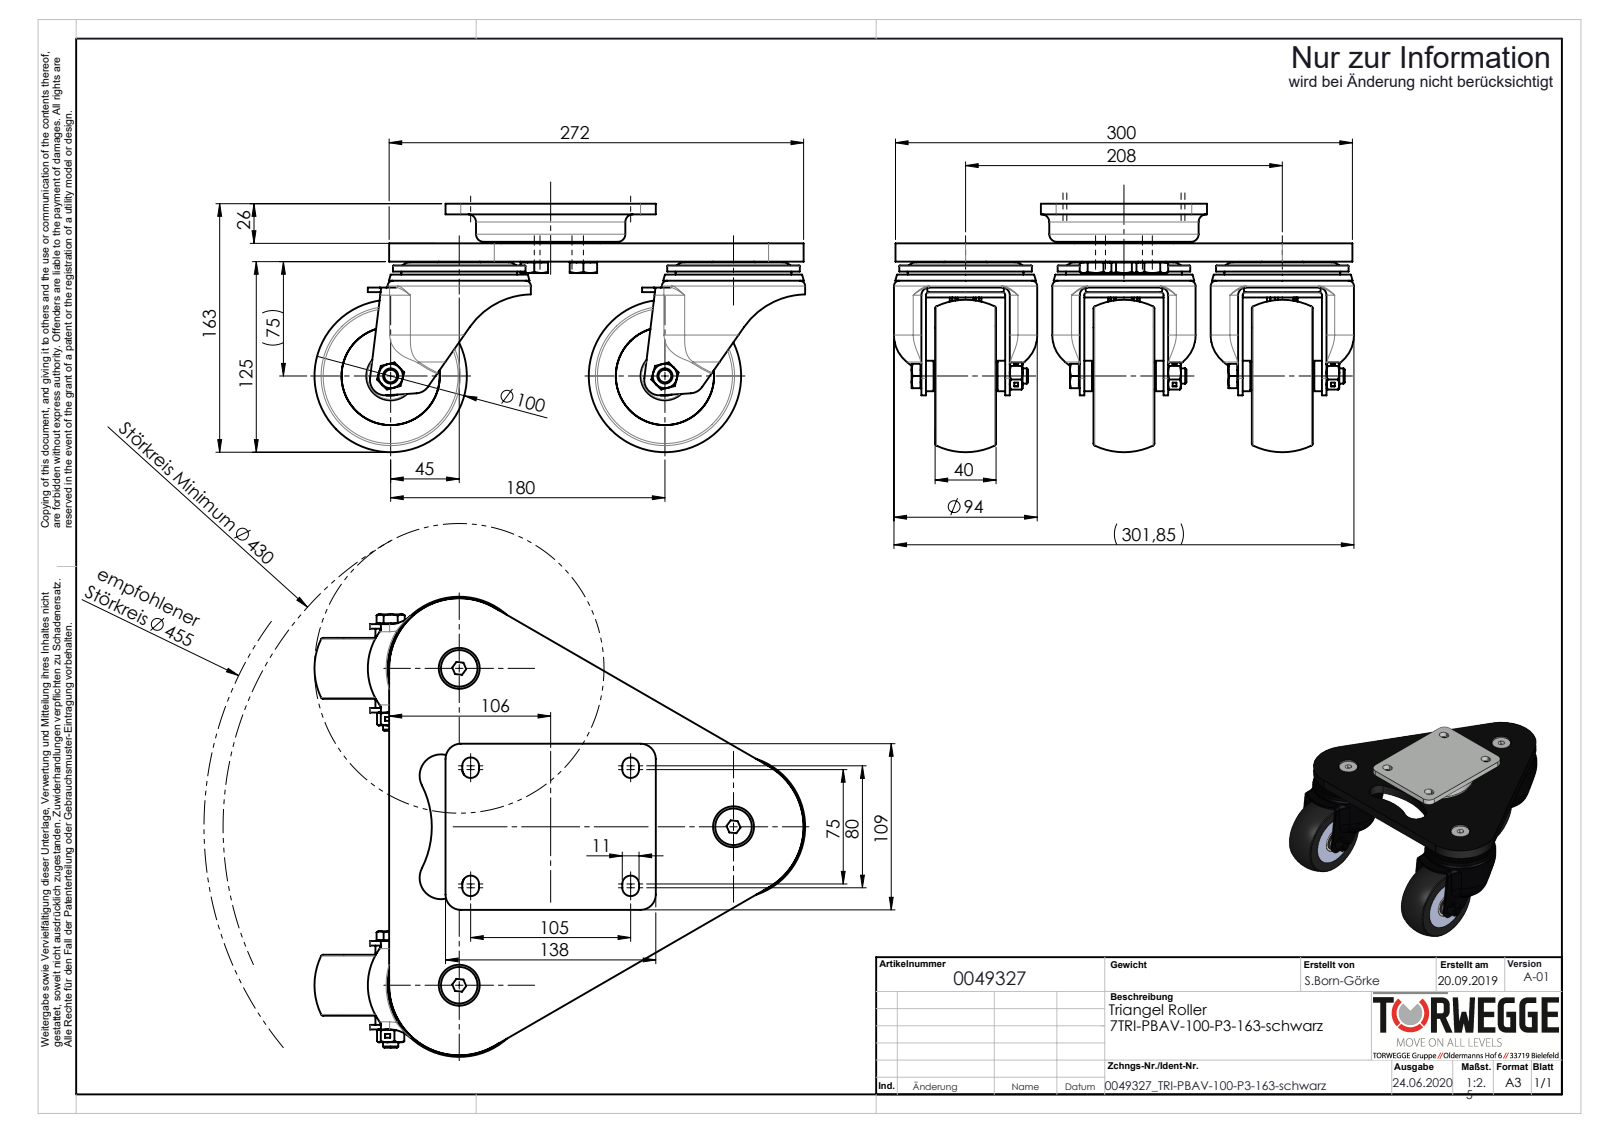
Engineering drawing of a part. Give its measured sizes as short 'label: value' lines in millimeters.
name: 0049327
written by: SolidWorks 2018 (AUTOMOTIVE_DESIGN)
unit: mm
bodies: 62 solids, 1324 faces (456 planar, 441 cylindrical, 427 other)
size: 322 × 301.85 × 163
volume: 2 136 000 mm³; area: 502 773 mm²
holes: 7× ⌀12, 6× ⌀10.2, 5× ⌀13, 3× ⌀12.7, 3× ⌀13.5, 3× ⌀30, 3× ⌀88, 2× ⌀8.5, 2× ⌀10, 2× ⌀10.02, 2× ⌀10.1, 2× ⌀26
bosses: 5× ⌀18, 3× ⌀94, 3× ⌀87, 3× ⌀76, 3× ⌀62, 3× ⌀28.5, 3× ⌀24, 3× ⌀11.79
rounds: 9× R5, 8× R5.5, 8× R10, 6× R2, 3× R41.04, 3× R46, 2× R14, 2× R50
face distances: 12, 103.92, 40, 207.84, 38, 26, 6, 9, 7, 63.92
hole spacings: 132.07, 37.24, 98.5, 207.84, 180
